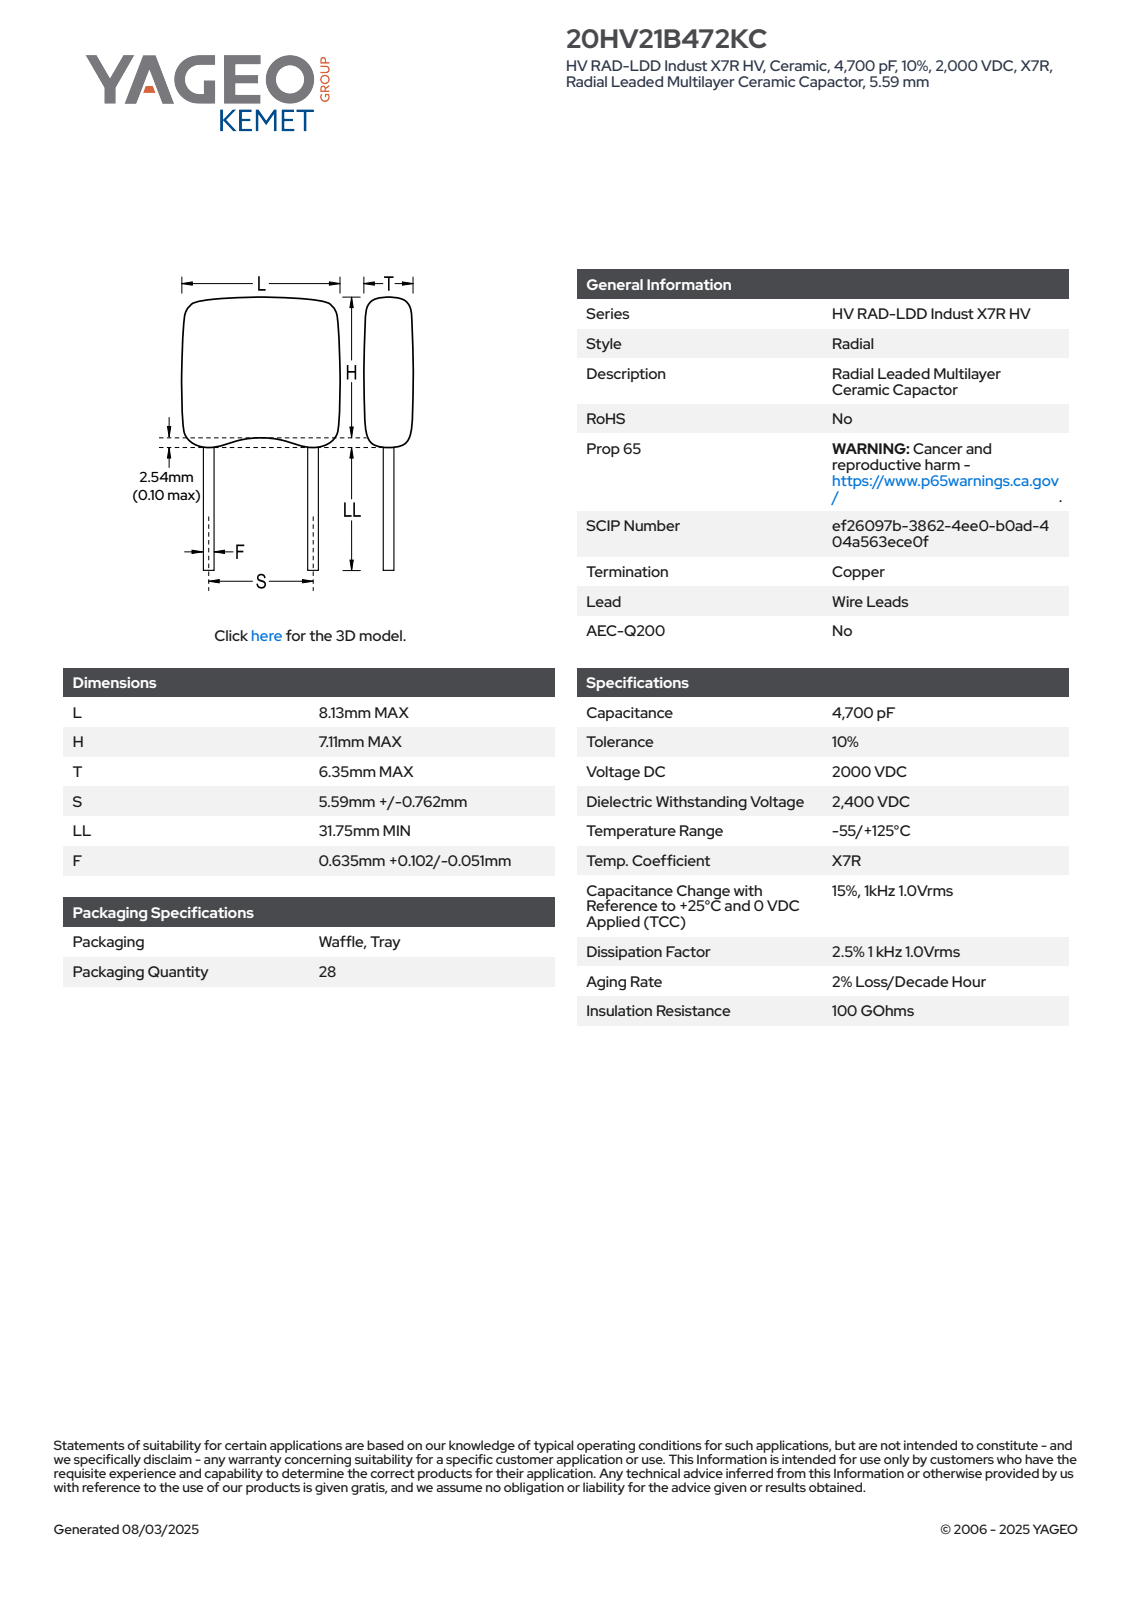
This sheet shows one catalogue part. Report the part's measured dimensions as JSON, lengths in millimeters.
{"part_name": "CCRM_RCST_HV21_L8.13H7.11T6.35S5.59LL3.175F0.737", "step_written_by": "SolidWorks 2021 (AUTOMOTIVE_DESIGN)", "units": "millimeters", "bodies": {"solids": 4, "faces": 92, "planar": 66, "cylindrical": 16, "other": 10}, "overall_size": [40.38, 8.13, 5.08], "volume_mm3": 323, "surface_area_mm2": 402, "round_bosses_or_shafts": [[0.64, 2]], "partial_cylinders_radius": [[0.5, 8], [2, 4]], "face_to_face_distances": [5.08, 8.13, 8.63, 31.75, 40.38, 3.64, 36.74, 4.99, 4.93, 35.45]}
